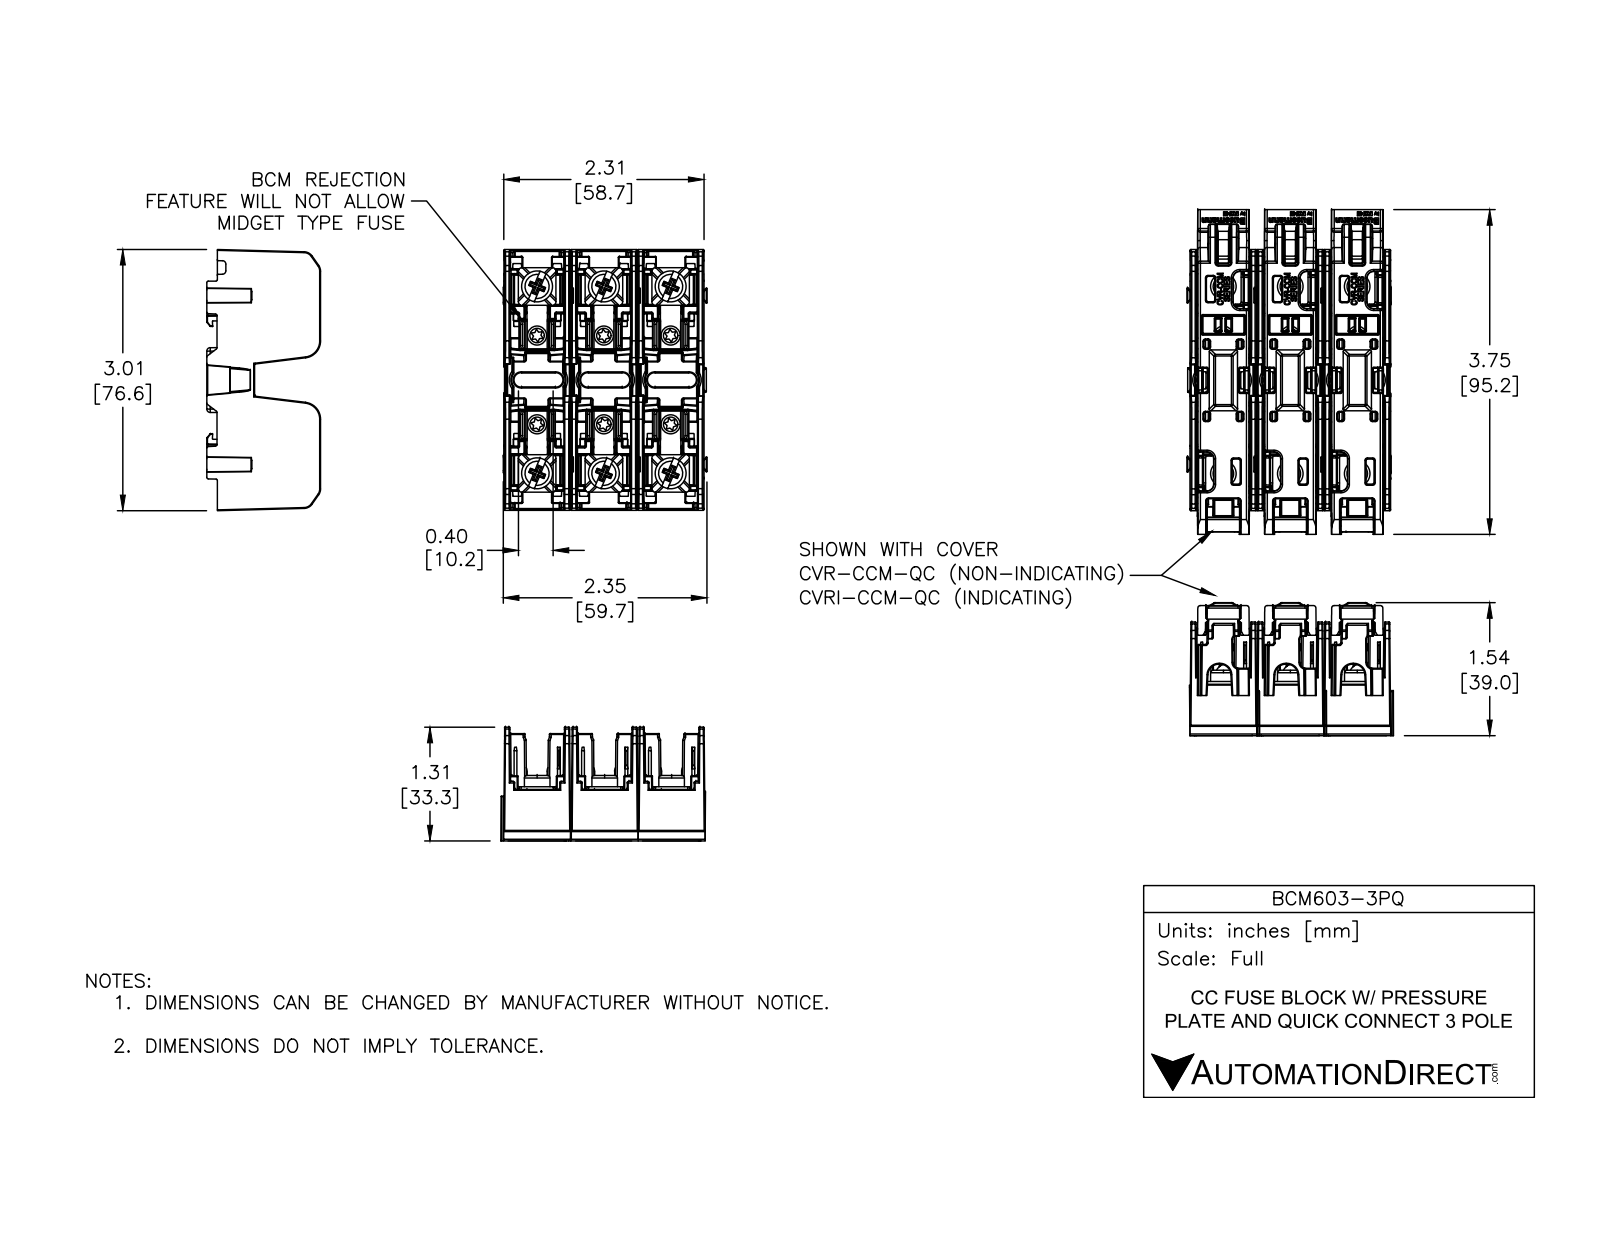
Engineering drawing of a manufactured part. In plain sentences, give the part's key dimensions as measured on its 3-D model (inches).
The part is named "BCM603-3PQ". Its 3-D file was written by "SolidWorks 2021 (CONFIG_CONTROL_DESIGN)". It is 13 solids with 1461 faces: 1026 planar, 277 cylindrical and 158 other. Overall it measures 3.015 by 2.346 by 1.312 inches. Its volume is 3.718 cubic inches and its surface area 77.69 square inches. Round holes: 6 of diameter 0.142, 4 of diameter 0.075. Round bosses or shafts: 6 of diameter 0.295, 4 of diameter 0.22, 4 of diameter 0.138. Partial cylindrical surfaces (rounded edges, fillets, slot ends): 36 of radius 0.004, 36 of radius 0.02, 6 of radius 0.03, 6 of radius 0.053, 6 of radius 0.061, 6 of radius 0.084, 6 of radius 0.085, 6 of radius 0.175. The main face-to-face distances are 0.768, 1.535, 0.691, 0.691, 0.594, 0.077, 0.077, 1.458, 1.459, 0.032. The hole center spacings are 0.768, 1.281, 1.025, 0.119, 1.535, 1.846, 2.232, 2.124.
